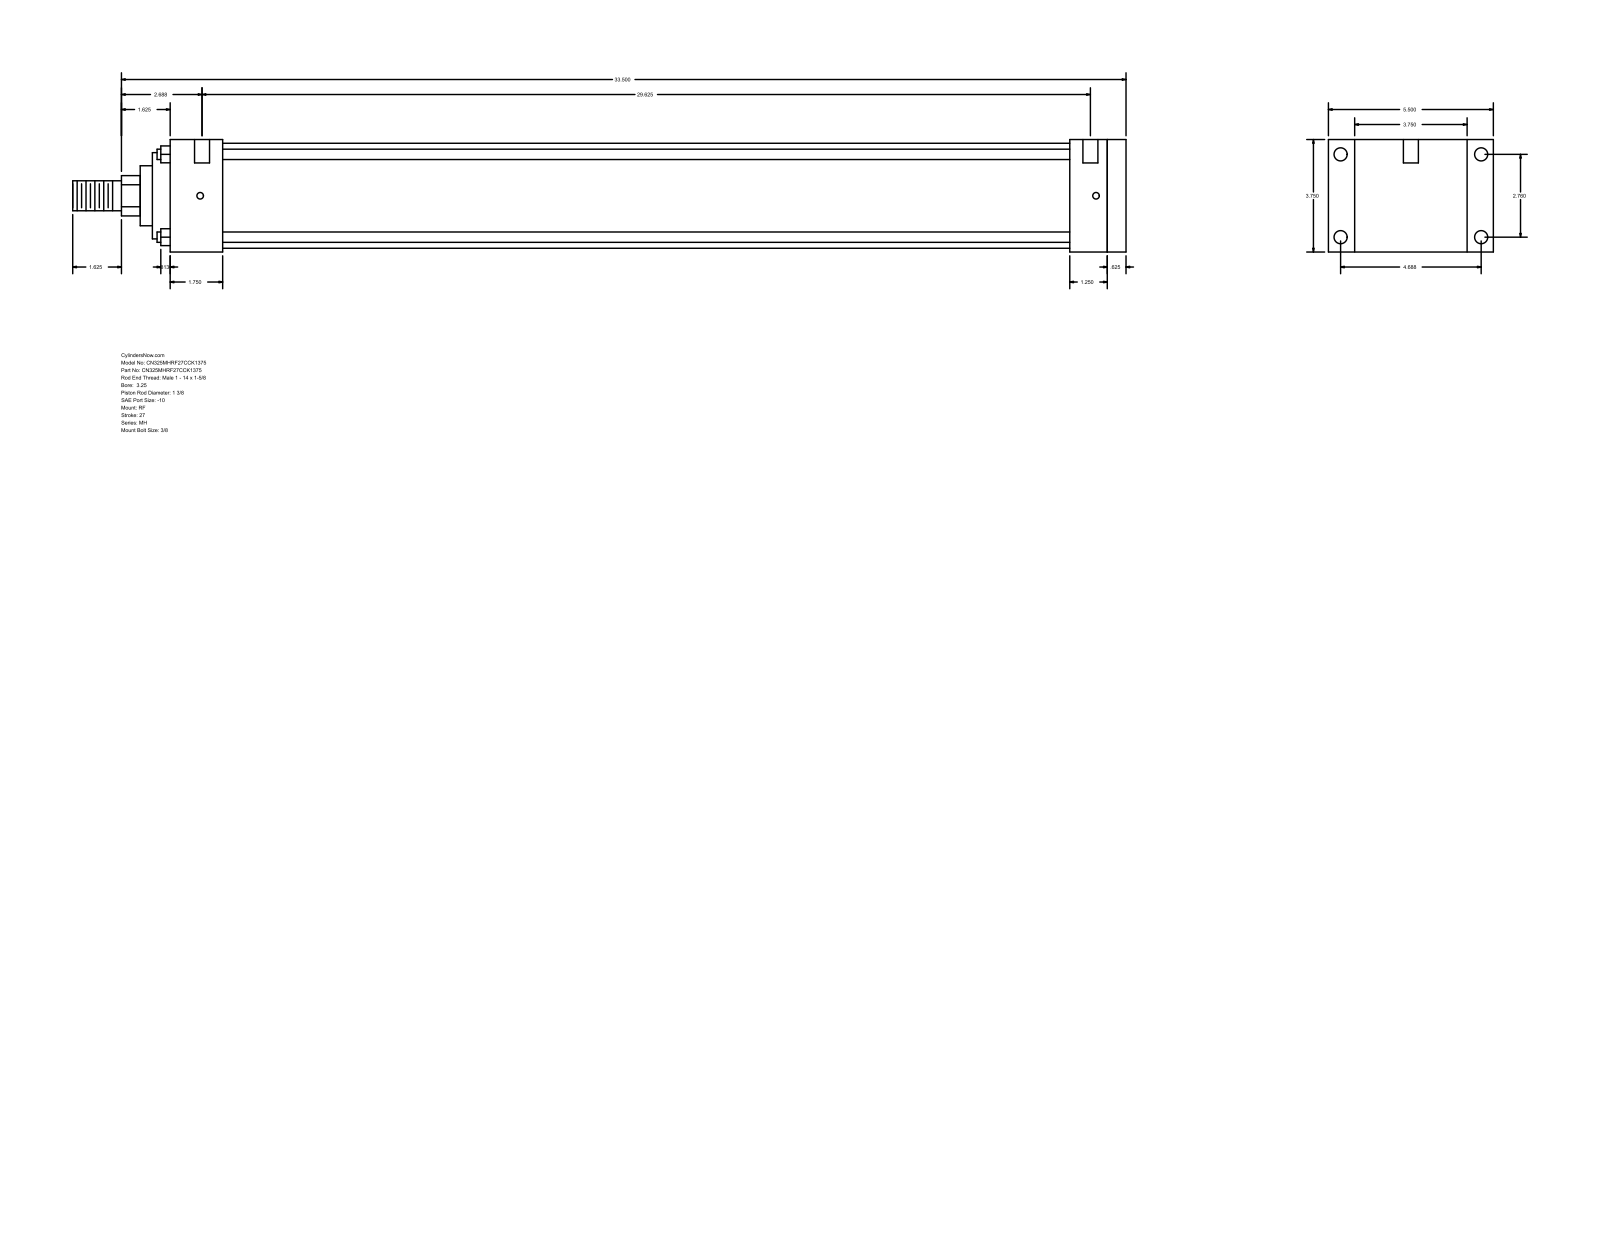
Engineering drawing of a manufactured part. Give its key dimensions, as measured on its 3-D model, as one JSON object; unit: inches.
{"part_name": "MH_RF__0325_1.375", "step_written_by": "GSSL Pune (CONFIG_CONTROL_DESIGN)", "units": "inches", "bodies": {"solids": 0, "faces": 94, "planar": 65, "cylindrical": 29, "other": 0}, "overall_size": [35.125, 5.5, 3.75], "round_holes": [[0.219, 4], [0.438, 4], [0.5, 2]], "round_bosses_or_shafts": [[0.345, 4], [3.5, 1], [2.875, 1], [2, 1], [1.375, 1], [1, 1]], "partial_cylinders_radius": [[0.672, 1]], "face_to_face_distances": [3.75, 31.875, 0.625, 31.25, 0.875, 4.625, 1.75, 29.5, 30.125, 30], "hole_center_spacings": [2.76, 4.687, 5.439, 29.875, 0.063, 0.187, 29.625, 29.688]}
